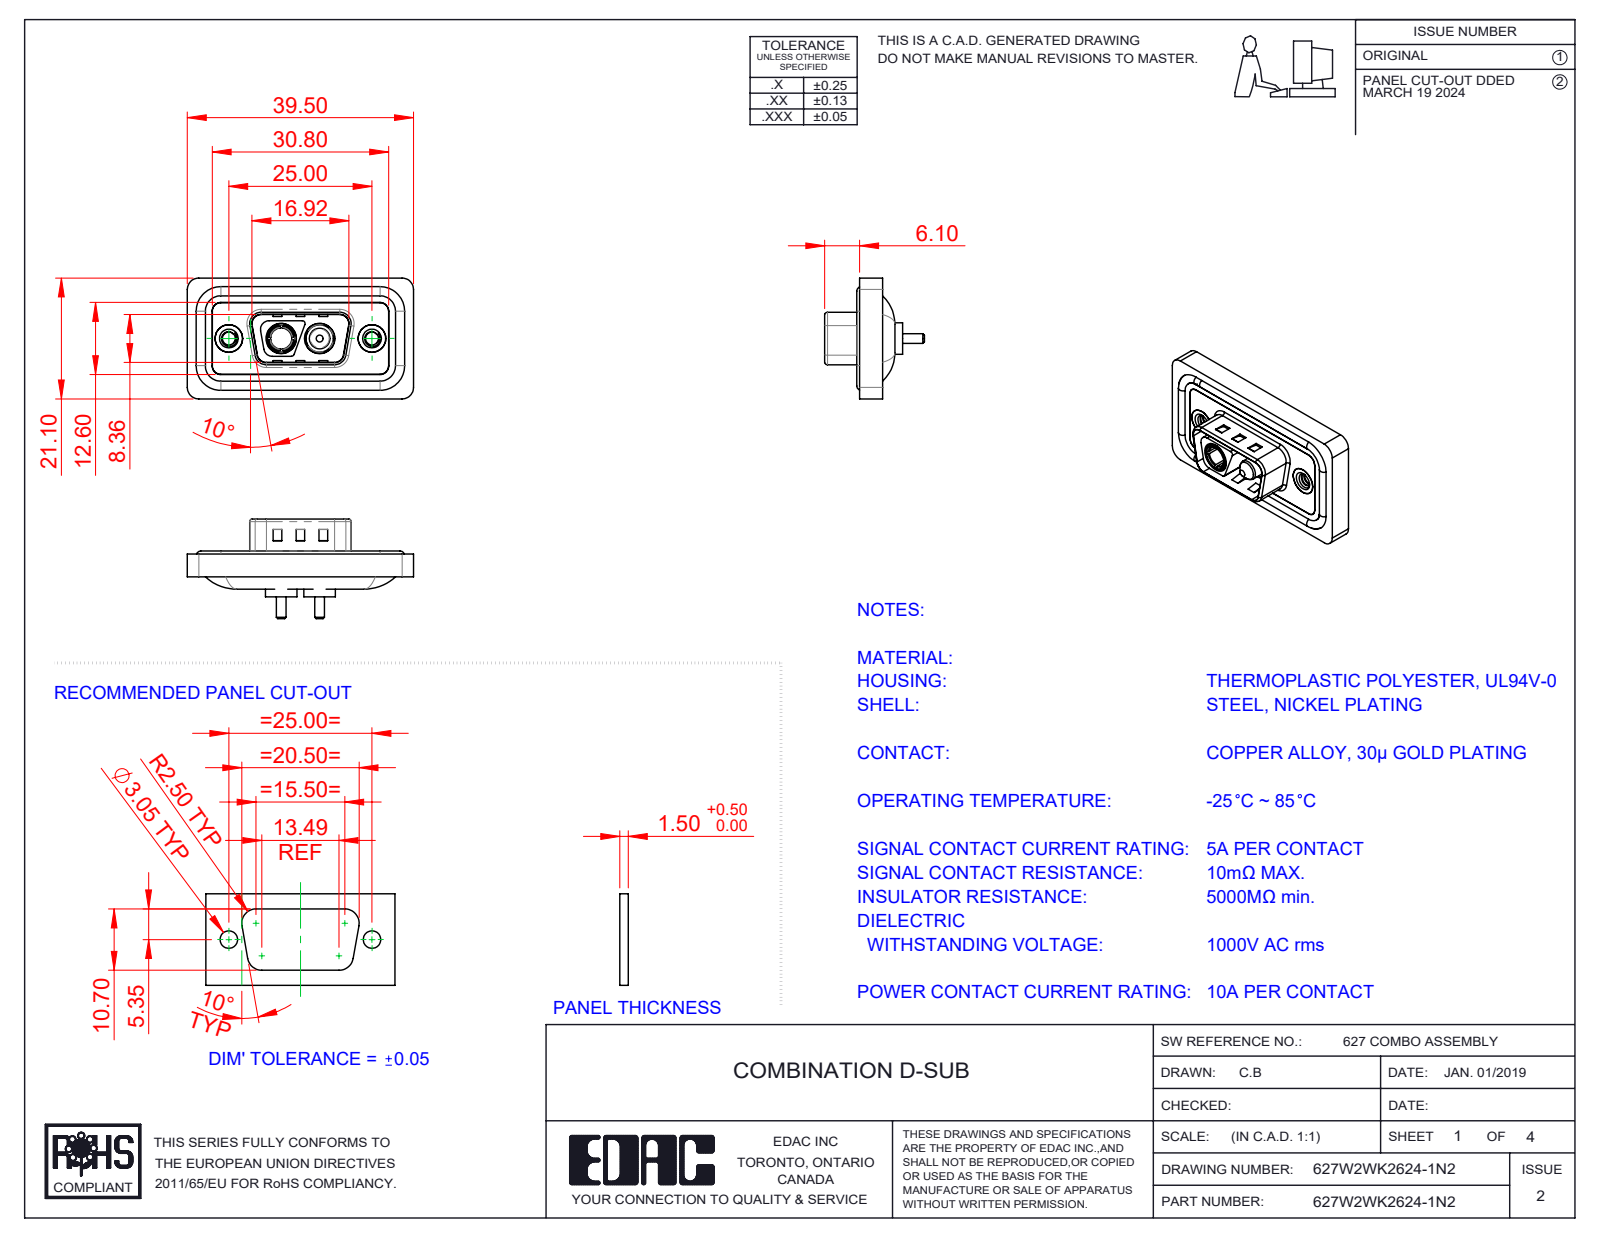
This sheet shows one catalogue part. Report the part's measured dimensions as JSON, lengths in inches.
{"part_name": "Power Socket_10A S; 627Combo Housing_2WK2; Power Pin_10A S; 627Combo Waterproof Housing_09 Contacts (+4 more)", "step_written_by": "SolidWorks 2023 (CONFIG_CONTROL_DESIGN)", "units": "inches", "bodies": {"solids": 11, "faces": 534, "planar": 189, "cylindrical": 227, "other": 118}, "overall_size": [1.555, 0.831, 0.685], "volume_in3": 0.276, "surface_area_in2": 11.34, "round_holes": [[0.089, 2], [0.157, 2], [0.189, 2], [0.191, 2], [0.197, 2], [0.209, 2], [0.146, 1]], "round_bosses_or_shafts": [[0.063, 4], [0.217, 2], [0.205, 2], [0.193, 2], [0.187, 2], [0.148, 2], [0.067, 2], [0.195, 1]], "partial_cylinders_radius": [[0.059, 24], [0.079, 18], [0.02, 10], [0.063, 8], [0.01, 4], [0.024, 4], [0.026, 4], [0.035, 4]], "face_to_face_distances": [0.016, 0.043, 0.114, 0.02, 0.122, 0.063, 0.059, 0.157, 0.098, 0.071], "hole_center_spacings": [0.36, 0.624, 0.265, 0.984]}
